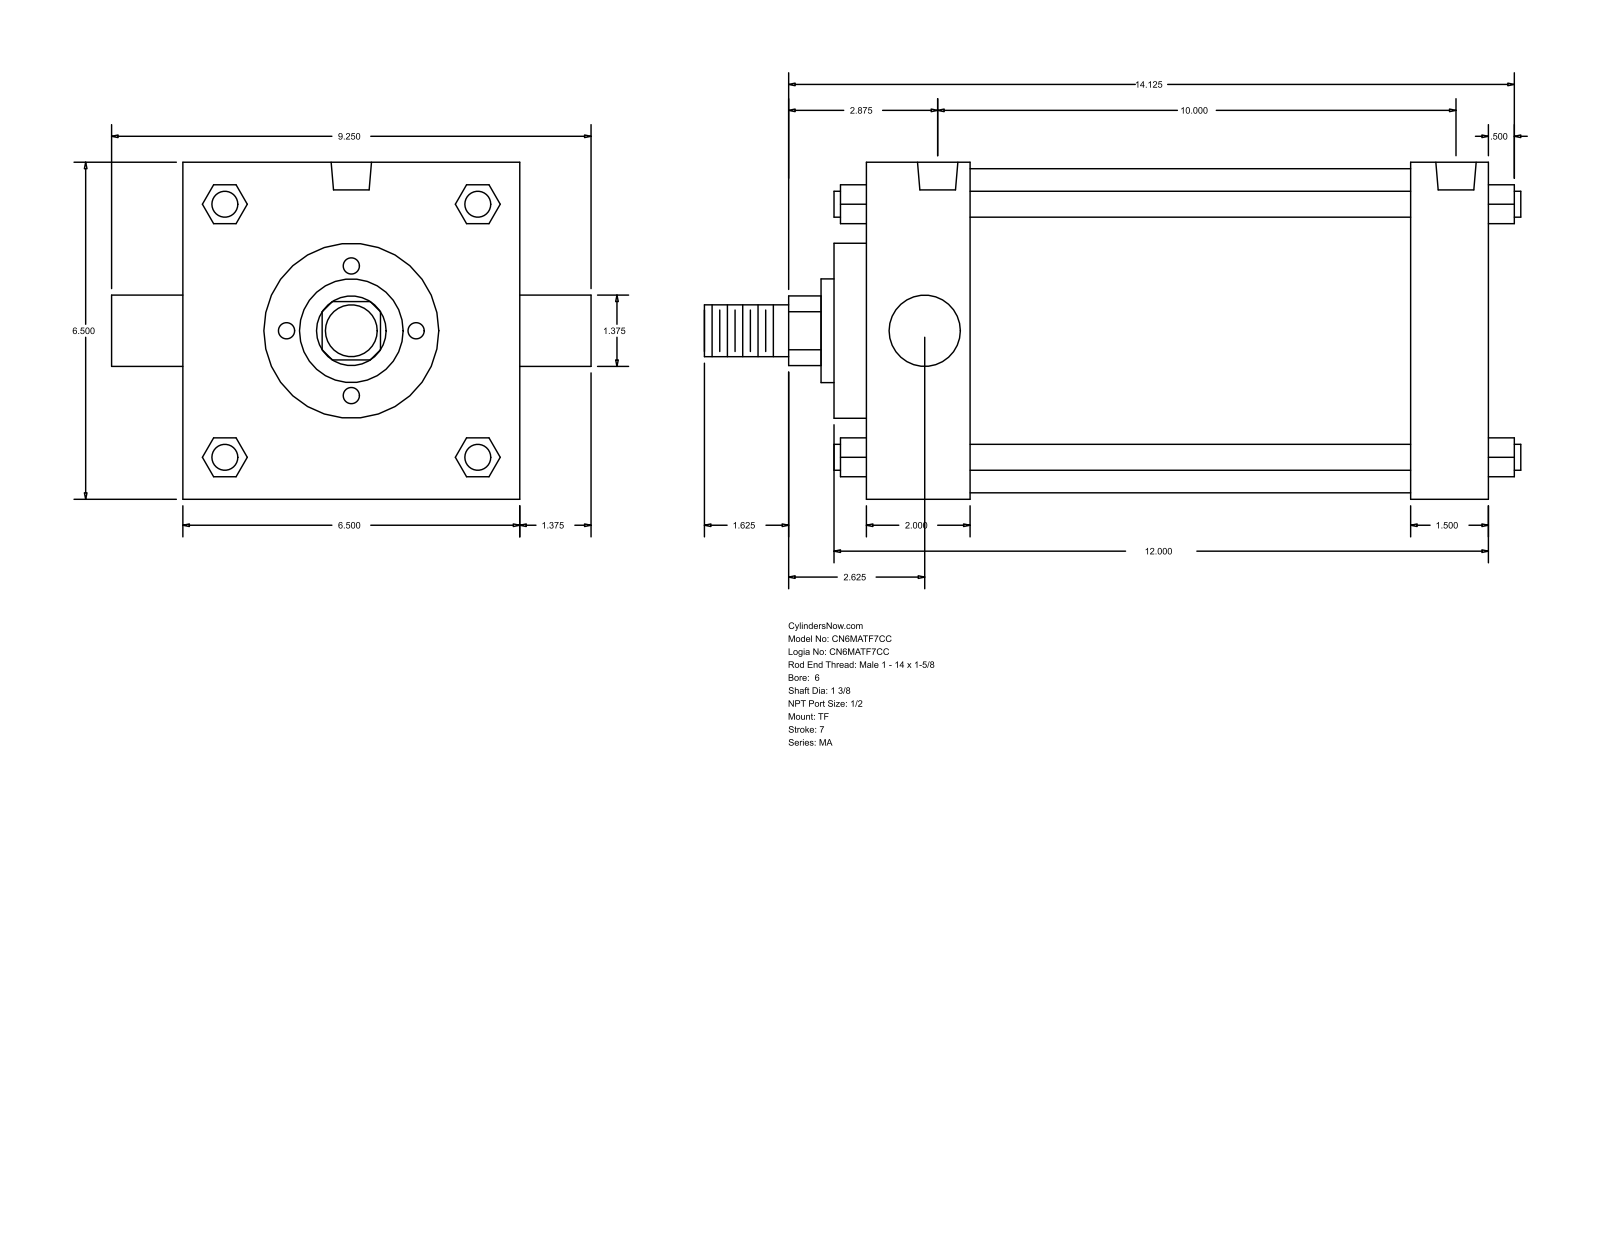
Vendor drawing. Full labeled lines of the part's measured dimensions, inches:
Part name (STEP PRODUCT): MA_TF__0600_1.375
STEP written by: GSSL Pune (CONFIG_CONTROL_DESIGN)
Units: inches
Bodies: 0 solids, 122 faces (93 planar, 29 cylindrical, 0 other)
Overall size (bounding box): 15.75 × 9.25 × 6.5
Round holes (diameter × count): ⌀0.687 ×3, ⌀0.778 ×2
Round bosses / shafts (diameter × count): ⌀0.5 ×4, ⌀1.375 ×2, ⌀6.25 ×1, ⌀3.375 ×1, ⌀2 ×1, ⌀1 ×1
Partial cylindrical surfaces — rounded edges, fillets, slot ends (radius × count): R0.672 ×1
Main face-to-face distances: 6.5, 12.125, 2, 10.125, 10.625, 8.625, 1.5, 2.625, 0.625, 11.25
Hole centre spacings: 0.125, 10, 10.125
